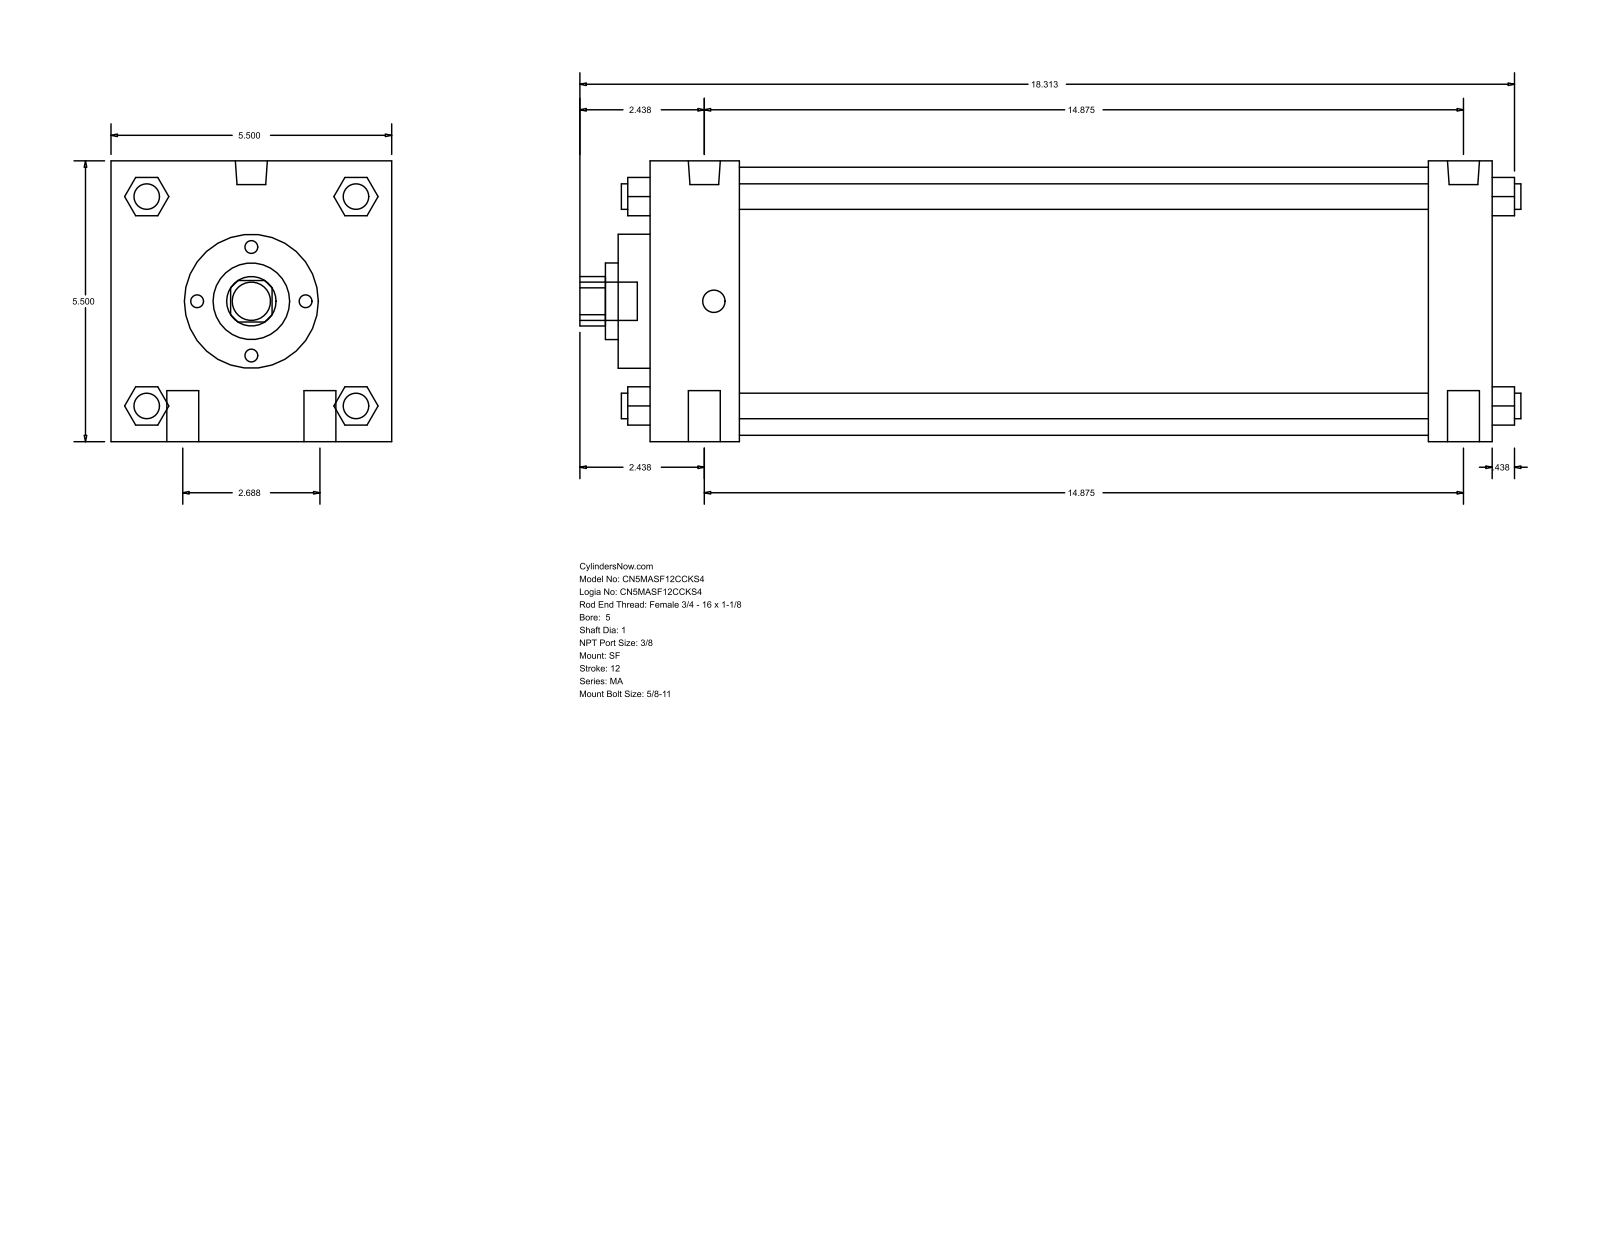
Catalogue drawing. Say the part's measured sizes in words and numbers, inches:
The part is named "MA_SF__0500_1". Its 3-D file was written by "GSSL Pune (CONFIG_CONTROL_DESIGN)". It is 0 solids with 126 faces: 95 planar, 31 cylindrical and 0 other. Overall it measures 18.437 by 5.5 by 5.5 inches. Round holes: 1 of diameter 1, 1 of diameter 1.5, 1 of diameter 2.625, 1 of diameter 5.25. Round bosses or shafts: 4 of diameter 0.625, 4 of diameter 0.5, 2 of diameter 0.627, 2 of diameter 0.437, 1 of diameter 0.75. Partial cylindrical surfaces (rounded edges, fillets, slot ends): 1 of radius 0.484. The main face-to-face distances are 5.5, 16.5, 1.75, 15.25, 13.5, 14.75, 1.25, 0.625, 2.375, 15.875.
